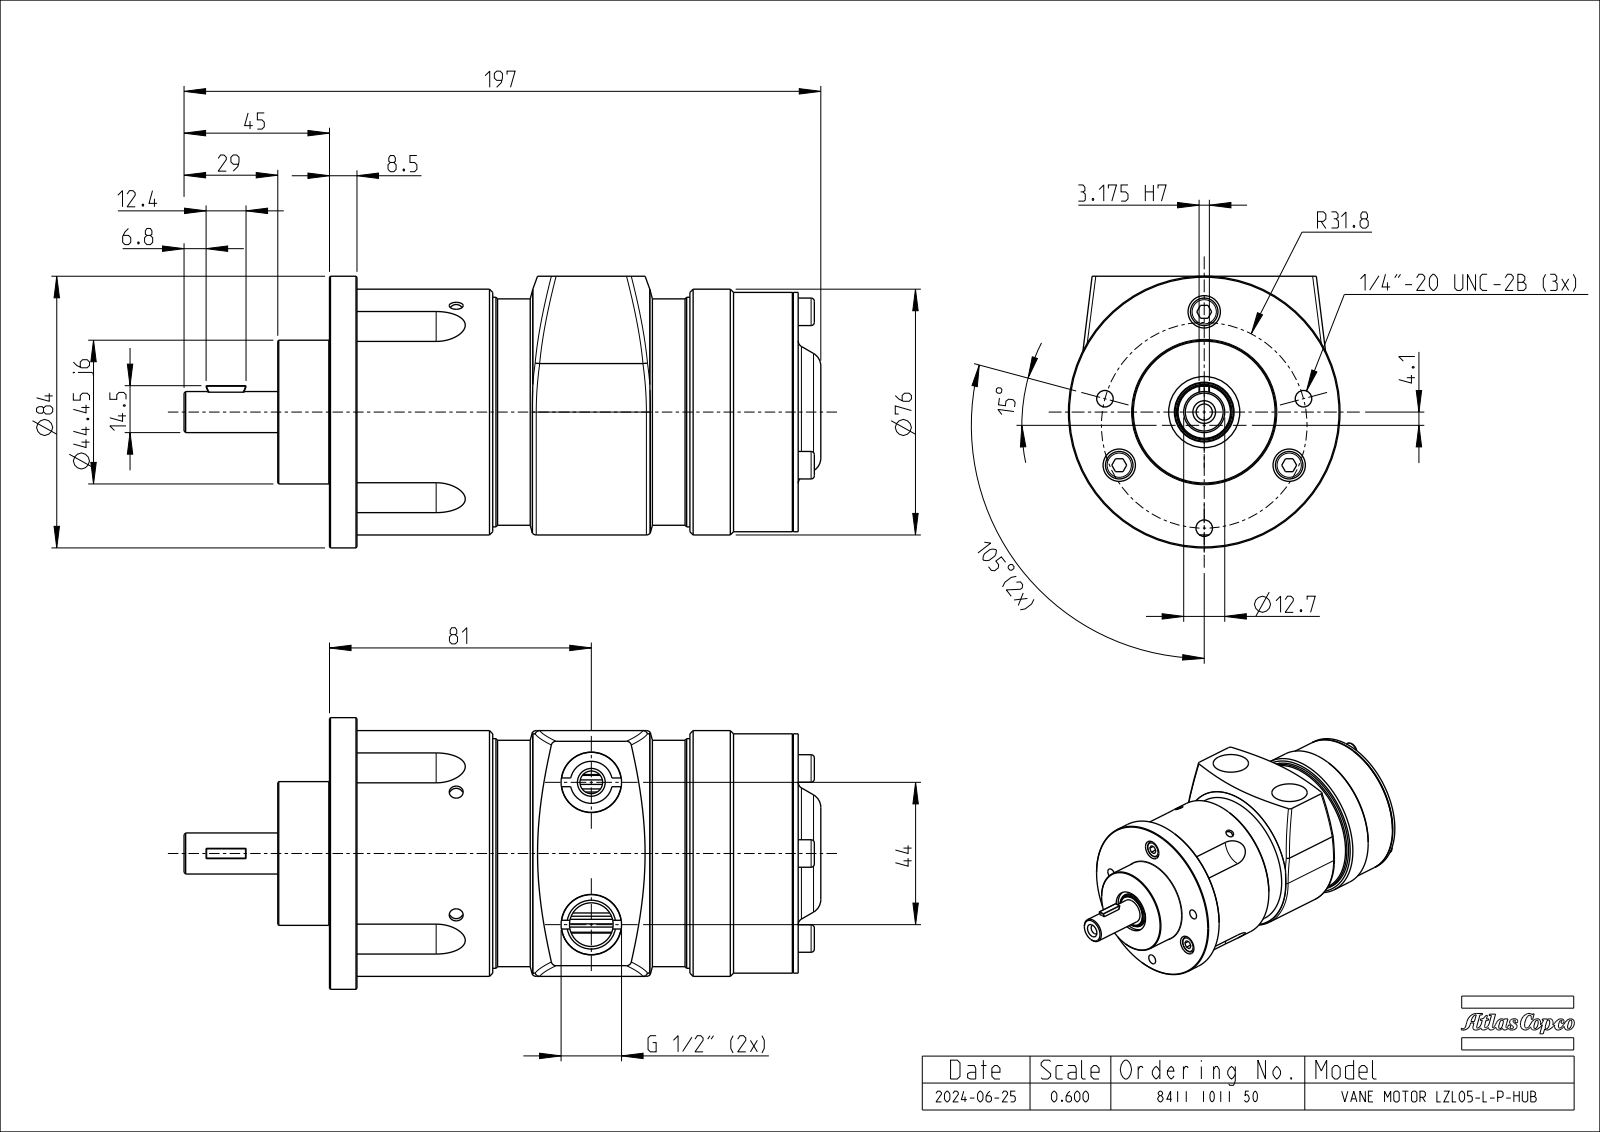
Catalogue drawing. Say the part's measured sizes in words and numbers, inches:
The part is named "8411101150_SW0001". Its 3-D file was written by "CREO PARAMETRIC BY PTC INC, 2022414 (AP242_MANAGED_MODEL_BASED_3D_ENGINEERING_MIM_LF)". It is 3 solids with 336 faces: 101 planar, 113 cylindrical and 122 other. Overall it measures 7.756 by 3.307 by 3.307 inches. Its volume is 42.24 cubic inches and its surface area 95.94 square inches. Round holes: 4 of diameter 0.169, 3 of diameter 0.201, 3 of diameter 0.394, 2 of diameter 0.157, 2 of diameter 0.177, 2 of diameter 0.315, 2 of diameter 0.736, 1 of diameter 0.197, 1 of diameter 0.276, 1 of diameter 0.512, 1 of diameter 0.866, 1 of diameter 0.945. Round bosses or shafts: 3 of diameter 0.335, 2 of diameter 0.236, 1 of diameter 3.307, 1 of diameter 2.992, 1 of diameter 2.913, 1 of diameter 2.795, 1 of diameter 2.756, 1 of diameter 1.75. Partial cylindrical surfaces (rounded edges, fillets, slot ends): 4 of radius 0.008, 4 of radius 0.394, 2 of radius 0.412, 1 of radius 0.25, 1 of radius 0.256. The main face-to-face distances are 5.709, 0.63, 0.335, 6.339, 5.374, 0.965, 5.65, 0.276, 5.984, 6.614. The hole center spacings are 1.22, 0.693, 1.181, 0.488, 0.623, 0.711, 0.828, 0.967.
